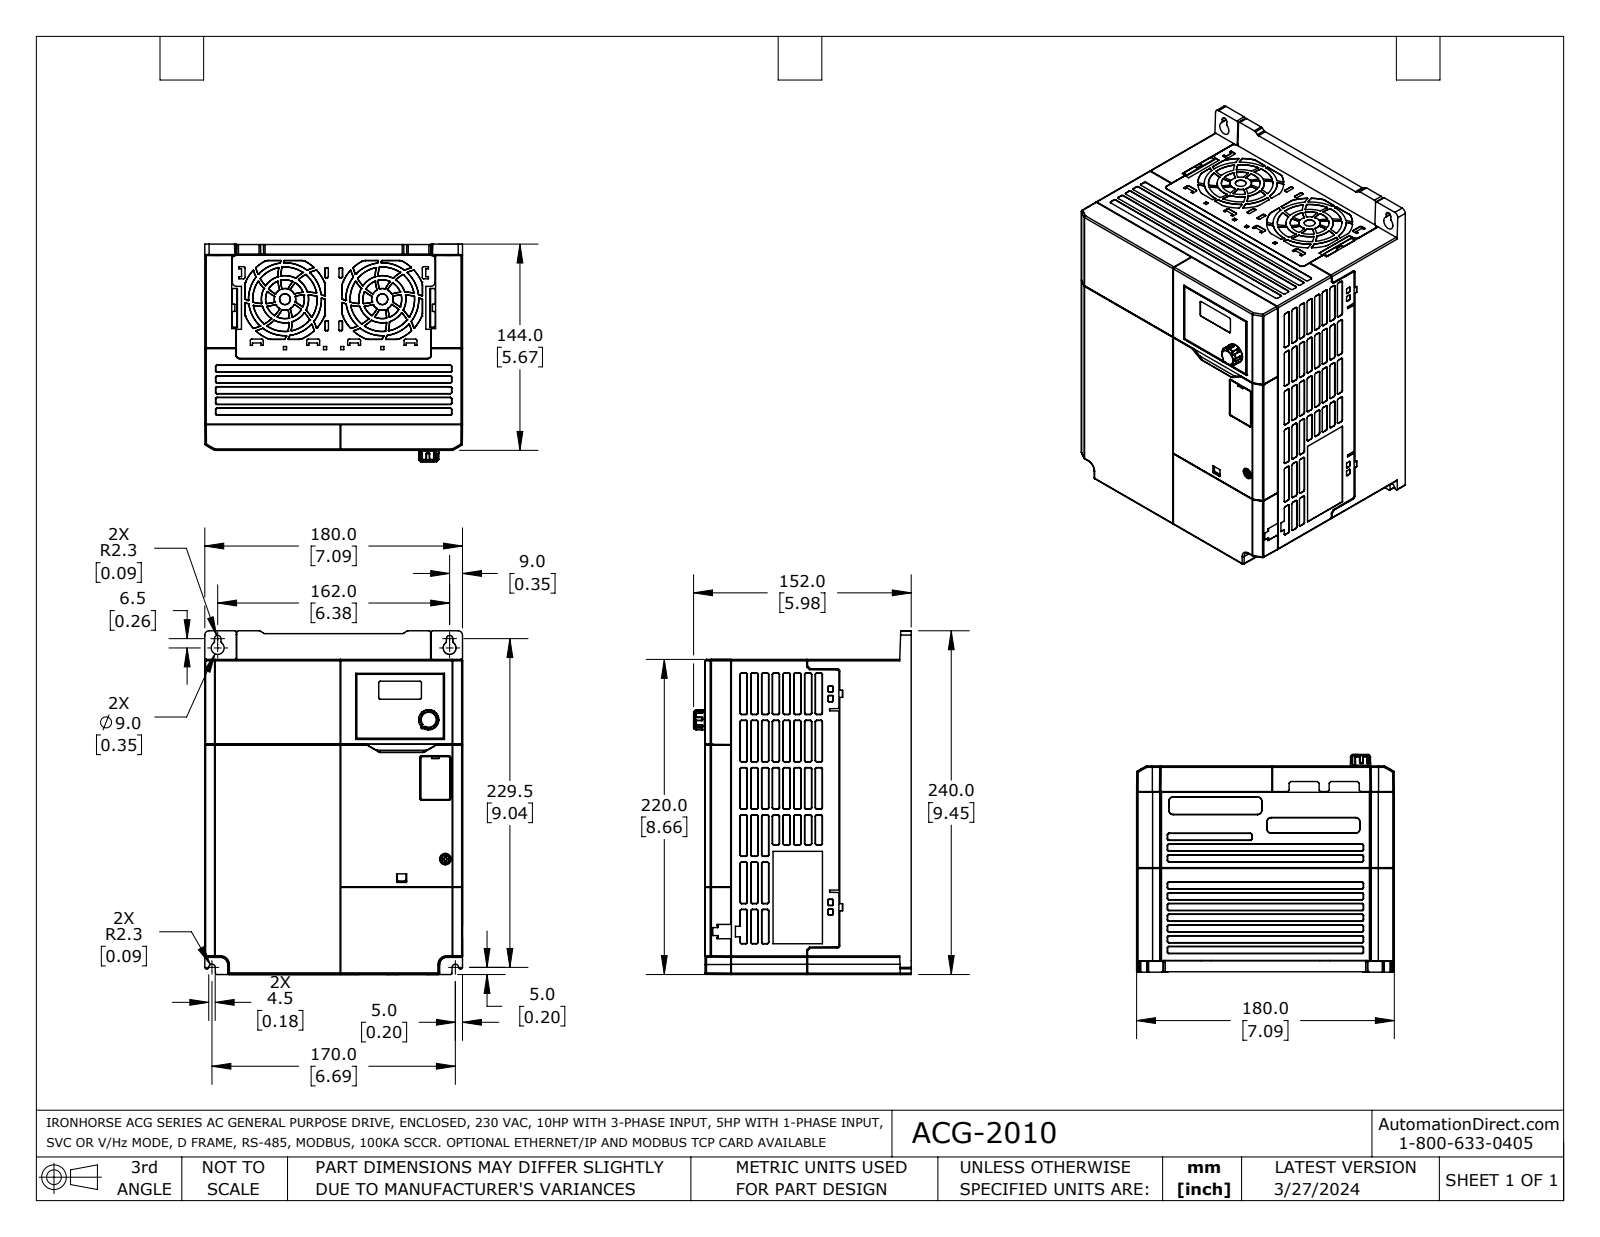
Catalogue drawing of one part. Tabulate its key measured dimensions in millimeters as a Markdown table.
| quantity | value |
| --- | --- |
| part name | ACG-2010 |
| STEP written by | SolidWorks 2021 (AUTOMOTIVE_DESIGN) |
| units | millimeters |
| bodies | 3 solids, 5218 faces (2417 planar, 929 cylindrical, 1872 other) |
| overall size | 240 × 180 × 152 |
| volume | 1 437 000 mm³ |
| surface area | 486 000 mm² |
| round holes (diameter × count) | 1 × 1, 7 × 1, 10.6 × 1, 12 × 1 |
| round bosses / shafts (diameter × count) | 14 × 1, 13.8 × 1, 6 × 1 |
| partial cylindrical surfaces (radius × count) | 0.5 × 587, 1 × 88, 0.2 × 65, 0.3 × 27, 0.6 × 16, 1.2 × 10, 2 × 5, 1.5 × 4 |
| main face-to-face distances | 135, 4.2, 139.2, 3.4, 135.8, 0.8, 1, 179, 3.2, 136 |
| hole center spacings | 7, 54.7, 55.7, 93.3, 98, 144.6 |
